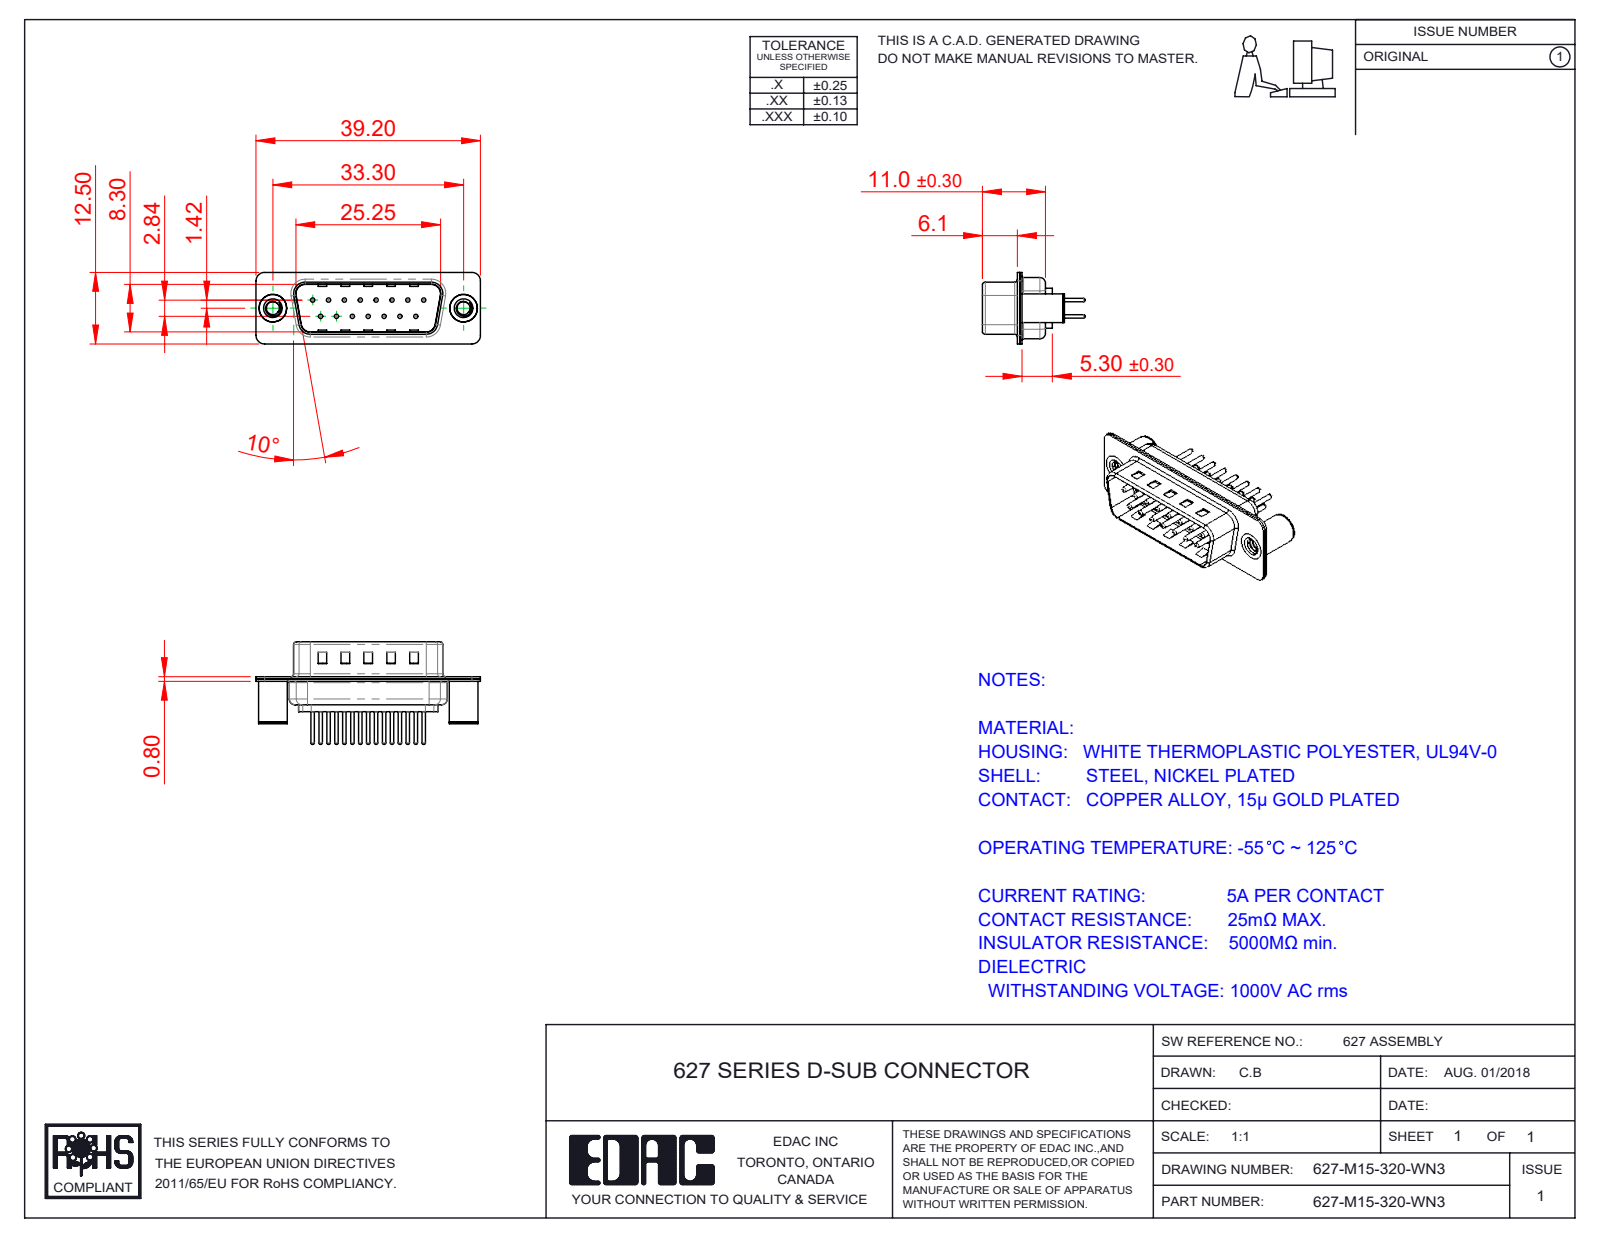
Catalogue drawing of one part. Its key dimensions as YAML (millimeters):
part_name: "627M Shell Front_15 Contacts; 627M Contact Row 2_20; 627M Housing_15 Contacts; 627M Shell Rear_15 Contacts (+3 more)"
step_written_by: "SolidWorks 2020 (CONFIG_CONTROL_DESIGN)"
units: millimeters
bodies: {solids: 20, faces: 929, planar: 244, cylindrical: 367, other: 318}
overall_size: [39.2, 17.9, 12.5]
volume: 1966
surface_area: 5067
round_holes:
  - {diameter: 0.75, count: 15}
  - {diameter: 1.6, count: 15}
  - {diameter: 2, count: 15}
  - {diameter: 2.26, count: 2}
  - {diameter: 3.26, count: 2}
  - {diameter: 4, count: 2}
  - {diameter: 4.8, count: 2}
round_bosses_or_shafts:
  - {diameter: 1.5, count: 15}
  - {diameter: 0.6, count: 15}
  - {diameter: 5, count: 2}
  - {diameter: 4.9, count: 2}
partial_cylinders:
  - {radius: 1.5, count: 16}
  - {radius: 2, count: 12}
  - {radius: 0.5, count: 8}
  - {radius: 1.6, count: 8}
  - {radius: 0.25, count: 4}
  - {radius: 0.6, count: 4}
  - {radius: 0.65, count: 4}
  - {radius: 0.9, count: 4}
face_to_face_distances: [0.4, 0.8, 9.5, 9.1, 8.7, 9.9, 1.2, 5.3, 6.1, 5.7]
hole_center_spacings: [3.16, 2.77, 5.54, 8.31, 11.08, 5.03, 5.04, 7.48]
